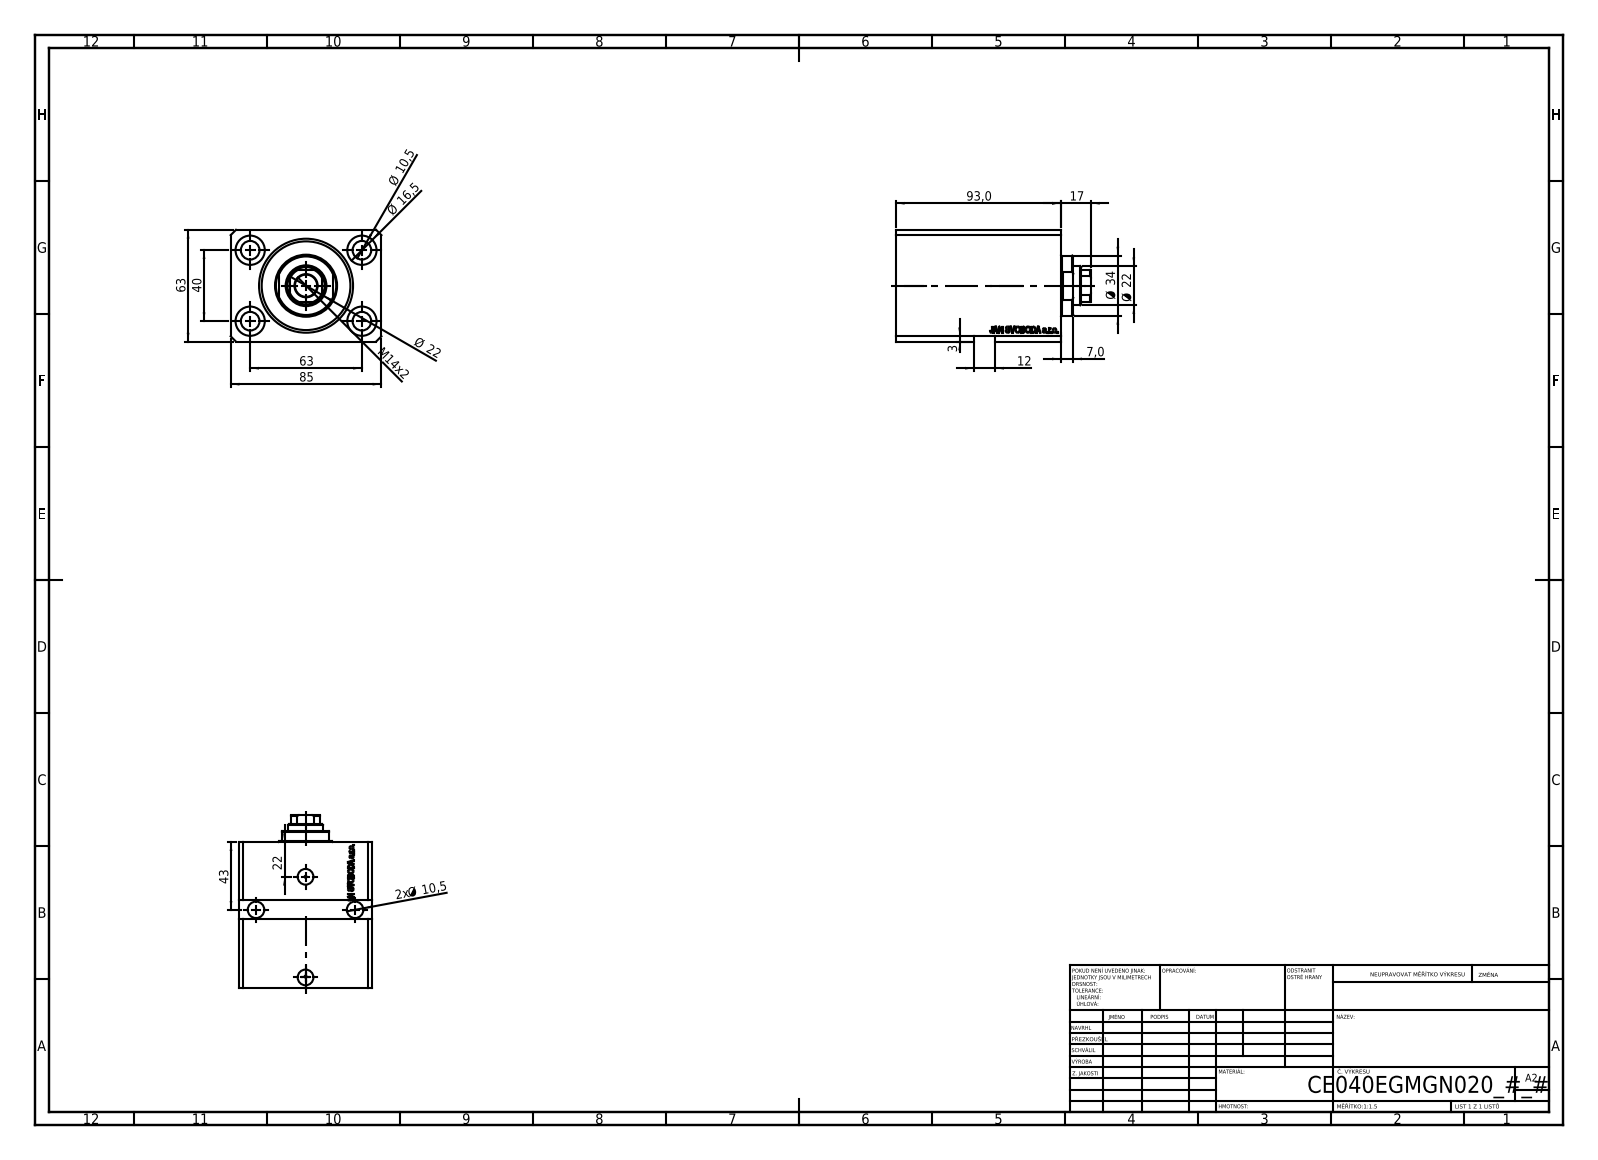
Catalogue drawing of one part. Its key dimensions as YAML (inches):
part_name: "V250CE_VC_E; V250CE_E_Body; V250CE_C_VCP"
step_written_by: "SolidWorks 2019 (CONFIG_CONTROL_DESIGN)"
units: inches
bodies: {solids: 3, faces: 917, planar: 459, cylindrical: 84, other: 374}
overall_size: [4.331, 3.346, 2.48]
volume: 26.07
surface_area: 135.2
round_holes:
  - {diameter: 0.413, count: 6}
  - {diameter: 0.049, count: 4}
  - {diameter: 0.65, count: 4}
  - {diameter: 0.394, count: 2}
  - {diameter: 0.518, count: 2}
  - {diameter: 0.787, count: 2}
  - {diameter: 0.492, count: 1}
  - {diameter: 0.866, count: 1}
  - {diameter: 1.575, count: 1}
  - {diameter: 2.087, count: 1}
round_bosses_or_shafts:
  - {diameter: 1.339, count: 1}
partial_cylinders:
  - {radius: 0.413, count: 1}
face_to_face_distances: [2.48, 3.346, 3.661, 0.669, 2.992, 0.449, 2.543, 3.213, 2.205, 1.756]
hole_center_spacings: [1.469, 2.48, 1.491, 1.575, 2.082, 2.098, 2.938, 0.021]
